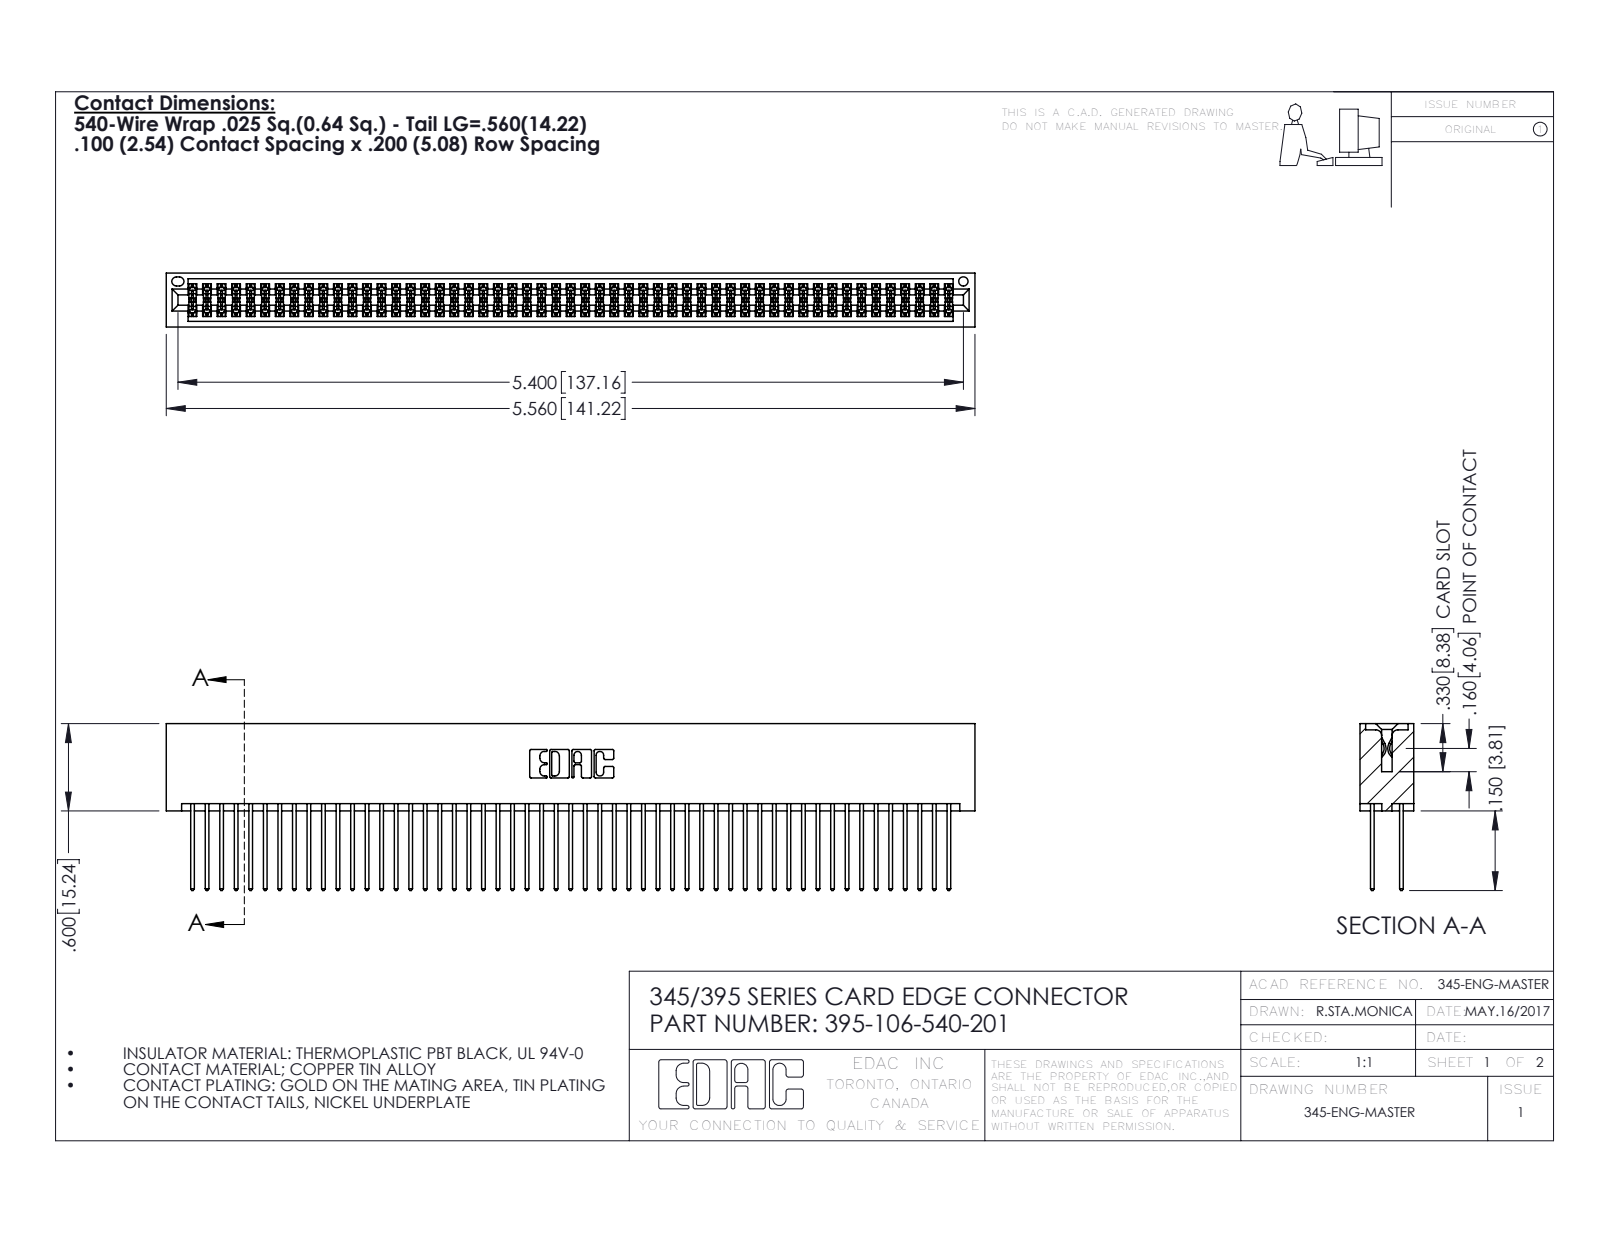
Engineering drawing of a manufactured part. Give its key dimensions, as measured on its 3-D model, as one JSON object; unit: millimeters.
{"part_name": "395-106-540-201; 345 Part_No Mounting Lugs; 345-292-001_345-293-140", "step_written_by": "SolidWorks 2016 (CONFIG_CONTROL_DESIGN)", "units": "millimeters", "bodies": {"solids": 107, "faces": 5418, "planar": 3574, "cylindrical": 1844, "other": 0}, "overall_size": [141.2, 29.1, 9.4], "volume_mm3": 14800, "surface_area_mm2": 24320, "round_holes": [[1.6, 1]], "partial_cylinders_radius": [[0.2, 159], [0.3, 106], [0.3, 22], [0.2, 6], [0.8, 6], [0.7, 3], [0.4, 2], [0.5, 2]], "face_to_face_distances": [7.6, 1.8, 5.1, 2.5, 6.9, 0.6, 5.7, 9.4, 4.4, 3.8]}
